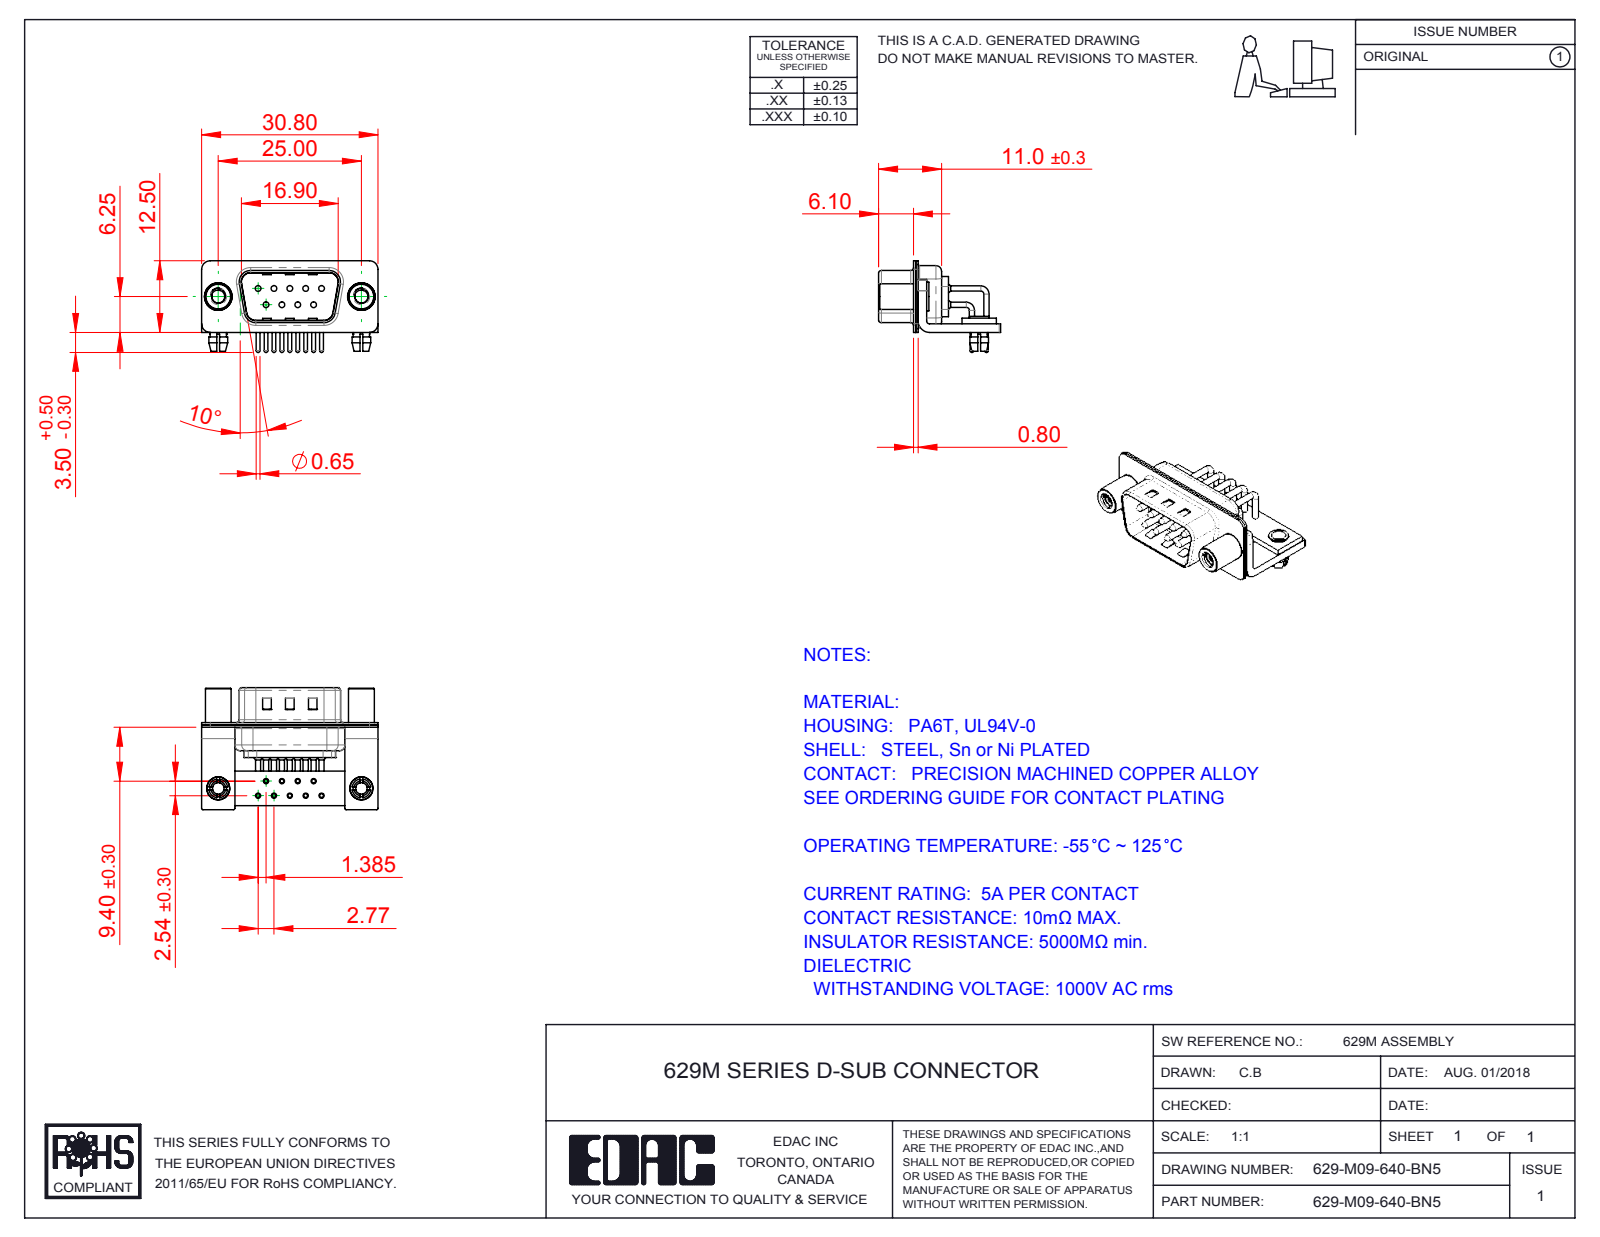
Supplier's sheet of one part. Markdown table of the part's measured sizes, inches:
| quantity | value |
| --- | --- |
| part name | 629M 4-40 Threaded Standoff; 629M Shell Rear_09 Contacts; 629M Shell Front_09 Contacts; 629M Housing_09 Contacts (+6 more) |
| STEP written by | SolidWorks 2016 (CONFIG_CONTROL_DESIGN) |
| units | inches |
| bodies | 19 solids, 1504 faces (759 planar, 567 cylindrical, 178 other) |
| overall size | 1.213 × 0.839 × 0.63 |
| volume | 0.121 in³ |
| surface area | 8.541 in² |
| round holes (diameter × count) | 0.079 × 11, 0.035 × 9, 0.039 × 9, 0.067 × 9, 0.089 × 2, 0.098 × 2, 0.126 × 2, 0.157 × 2, 0.189 × 2 |
| round bosses / shafts (diameter × count) | 0.059 × 9, 0.035 × 9, 0.026 × 9, 0.197 × 2, 0.193 × 2, 0.177 × 2, 0.157 × 2, 0.134 × 2 |
| partial cylindrical surfaces (radius × count) | 0.01 × 16, 0.059 × 16, 0.079 × 13, 0.02 × 9, 0.04 × 9, 0.063 × 8, 0.024 × 4, 0.026 × 4 |
| main face-to-face distances | 0.016, 0.059, 0.031, 0.033, 0.049, 0.075, 0.039, 0.098, 0.409, 0.376 |
| hole center spacings | 0.109, 0.218, 0.124, 0.192, 0.327, 0.114, 0.114, 0.198 |
